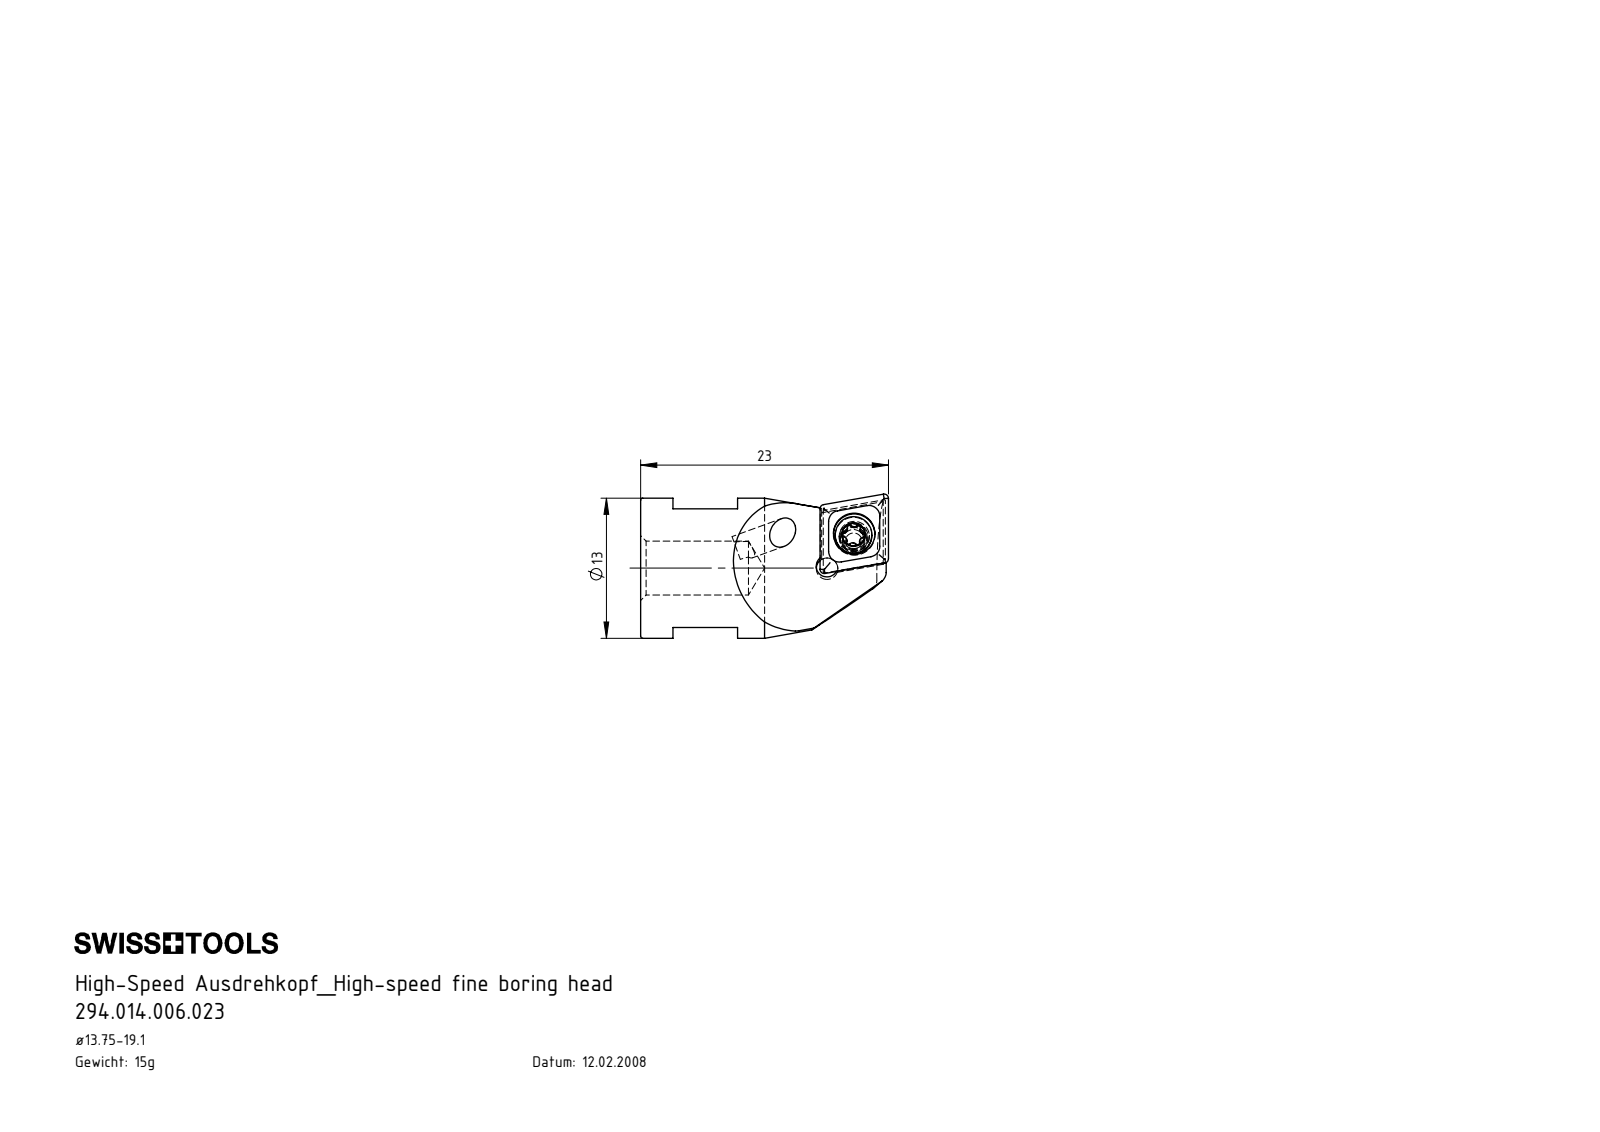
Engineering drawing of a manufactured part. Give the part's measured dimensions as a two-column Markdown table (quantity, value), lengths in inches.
| quantity | value |
| --- | --- |
| part name | HS6.A14.K11.023; CCMT060204; WCA-ER2.001.006_A; HS6-A14.K11.023_B |
| STEP written by | SolidWorks 2017 (AUTOMOTIVE_DESIGN) |
| units | inches |
| bodies | 3 solids, 126 faces (34 planar, 35 cylindrical, 57 other) |
| overall size | 0.906 × 0.527 × 0.512 |
| volume | 0.116 in³ |
| surface area | 2.209 in² |
| round holes (diameter × count) | 0.079 × 1, 0.081 × 1, 0.098 × 1, 0.11 × 1, 0.152 × 1, 0.197 × 1 |
| round bosses / shafts (diameter × count) | 0.512 × 1, 0.134 × 1, 0.098 × 1 |
| partial cylindrical surfaces (radius × count) | 0.008 × 6, 0.014 × 5, 0.014 × 1, 0.02 × 1, 0.039 × 1 |
| main face-to-face distances | 0.433, 0.089, 0.236, 0.094, 0.354, 0.118, 0.661, 0.543, 0.307, 0.058 |
| hole center spacings | 0.151, 0.155 |
